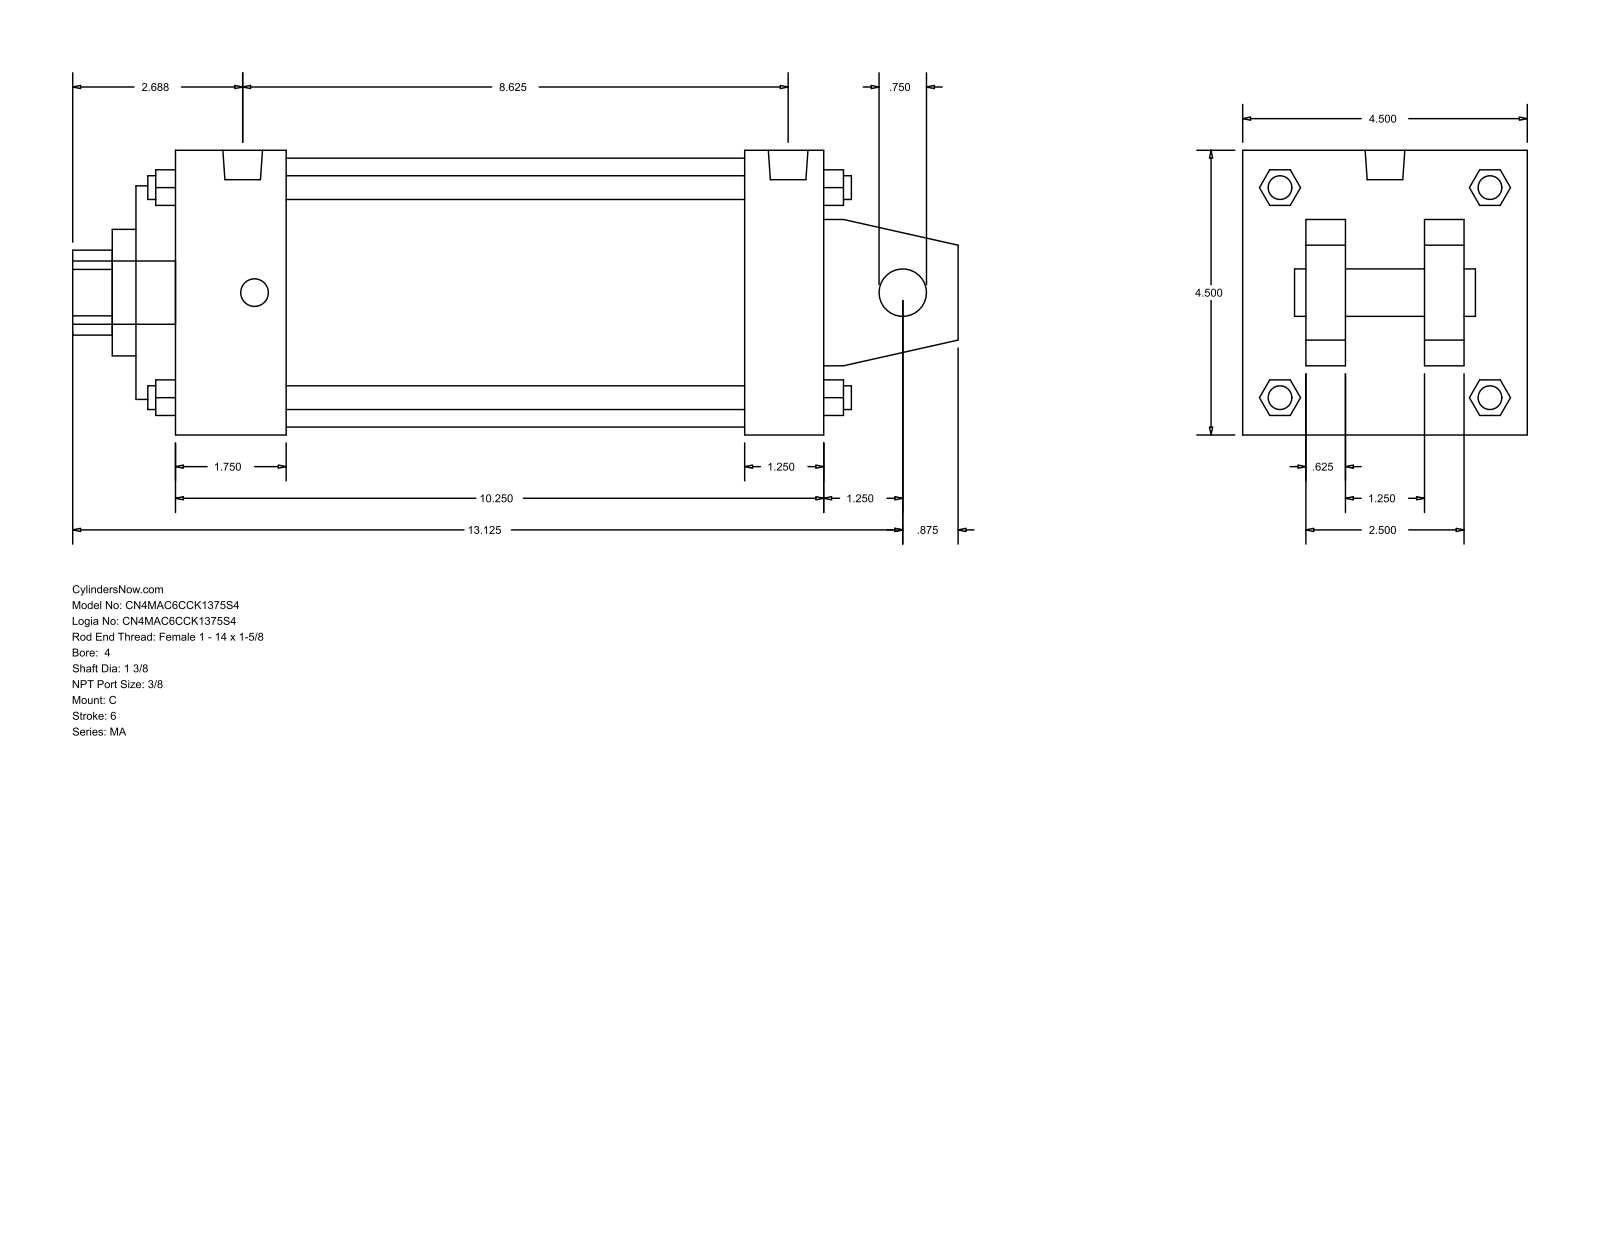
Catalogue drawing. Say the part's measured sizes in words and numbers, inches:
The part is named "MA_C__0400_1.375". Its 3-D file was written by "GSSL Pune (CONFIG_CONTROL_DESIGN)". It is 0 solids with 141 faces: 109 planar, 32 cylindrical and 0 other. Overall it measures 14 by 4.5 by 4.5 inches. Round holes: 1 of diameter 0.75, 1 of diameter 1.375, 1 of diameter 2, 1 of diameter 3.375, 1 of diameter 4.25. Round bosses or shafts: 4 of diameter 0.437, 4 of diameter 0.375, 2 of diameter 0.627, 1 of diameter 1. Partial cylindrical surfaces (rounded edges, fillets, slot ends): 1 of radius 0.672. The main face-to-face distances are 4.5, 0.625, 10.25, 2.875, 1.625, 1, 3.5, 1.875, 10.875, 9.625.
